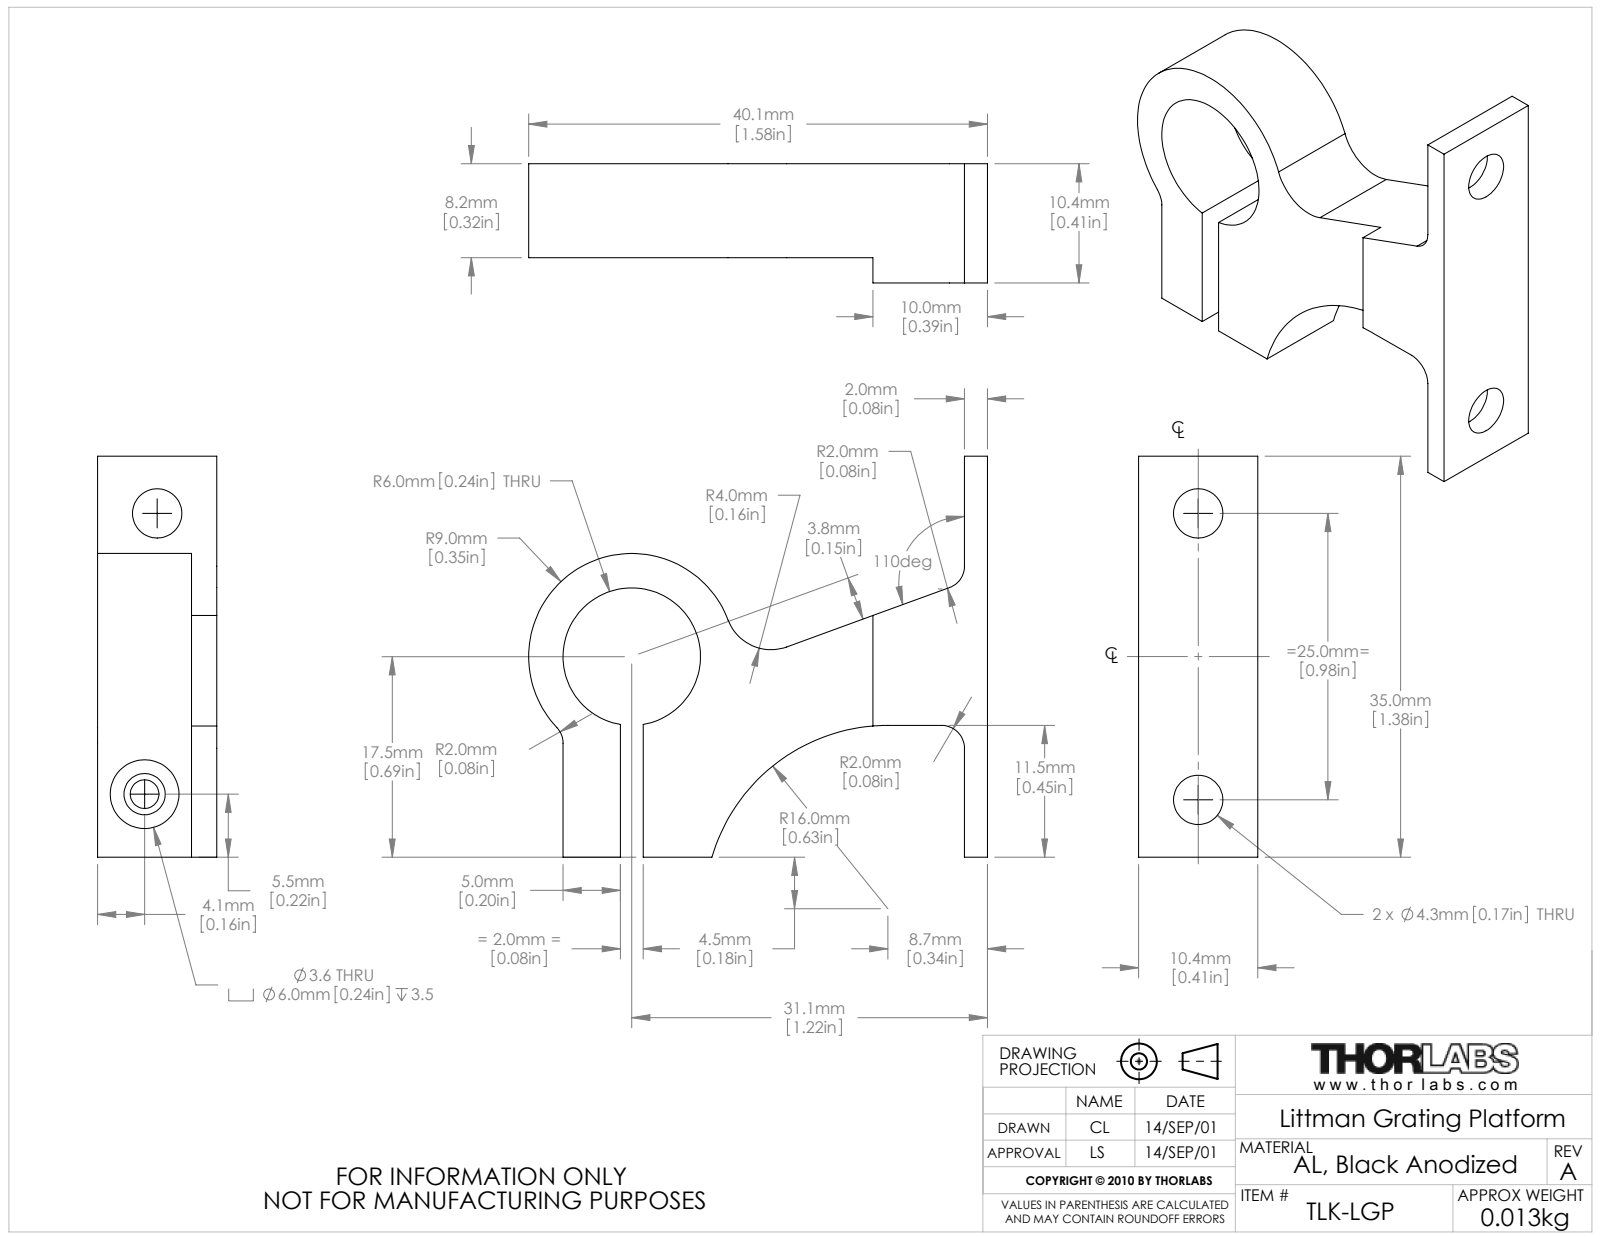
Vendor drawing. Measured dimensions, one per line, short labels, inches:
name: MEC 100 0024 G Littman grating platform
written by: SolidWorks 2009 (CONFIG_CONTROL_DESIGN)
unit: in
bodies: 1 solid, 37 faces (17 planar, 18 cylindrical, 2 other)
size: 1.577 × 1.378 × 0.409
volume: 0.281 in³; area: 5.005 in²
holes: 2× ⌀0.169, 1× ⌀0.098, 1× ⌀0.142, 1× ⌀0.236, 1× ⌀0.472
rounds: 3× R0.079, 1× R0.157, 1× R0.354, 1× R0.63
face distances: 0.323, 0.079, 1.183, 0.409, 0.087, 1.104, 1.262, 0.197, 0.276, 1.38
hole spacings: 0.048, 0.965, 0.984
